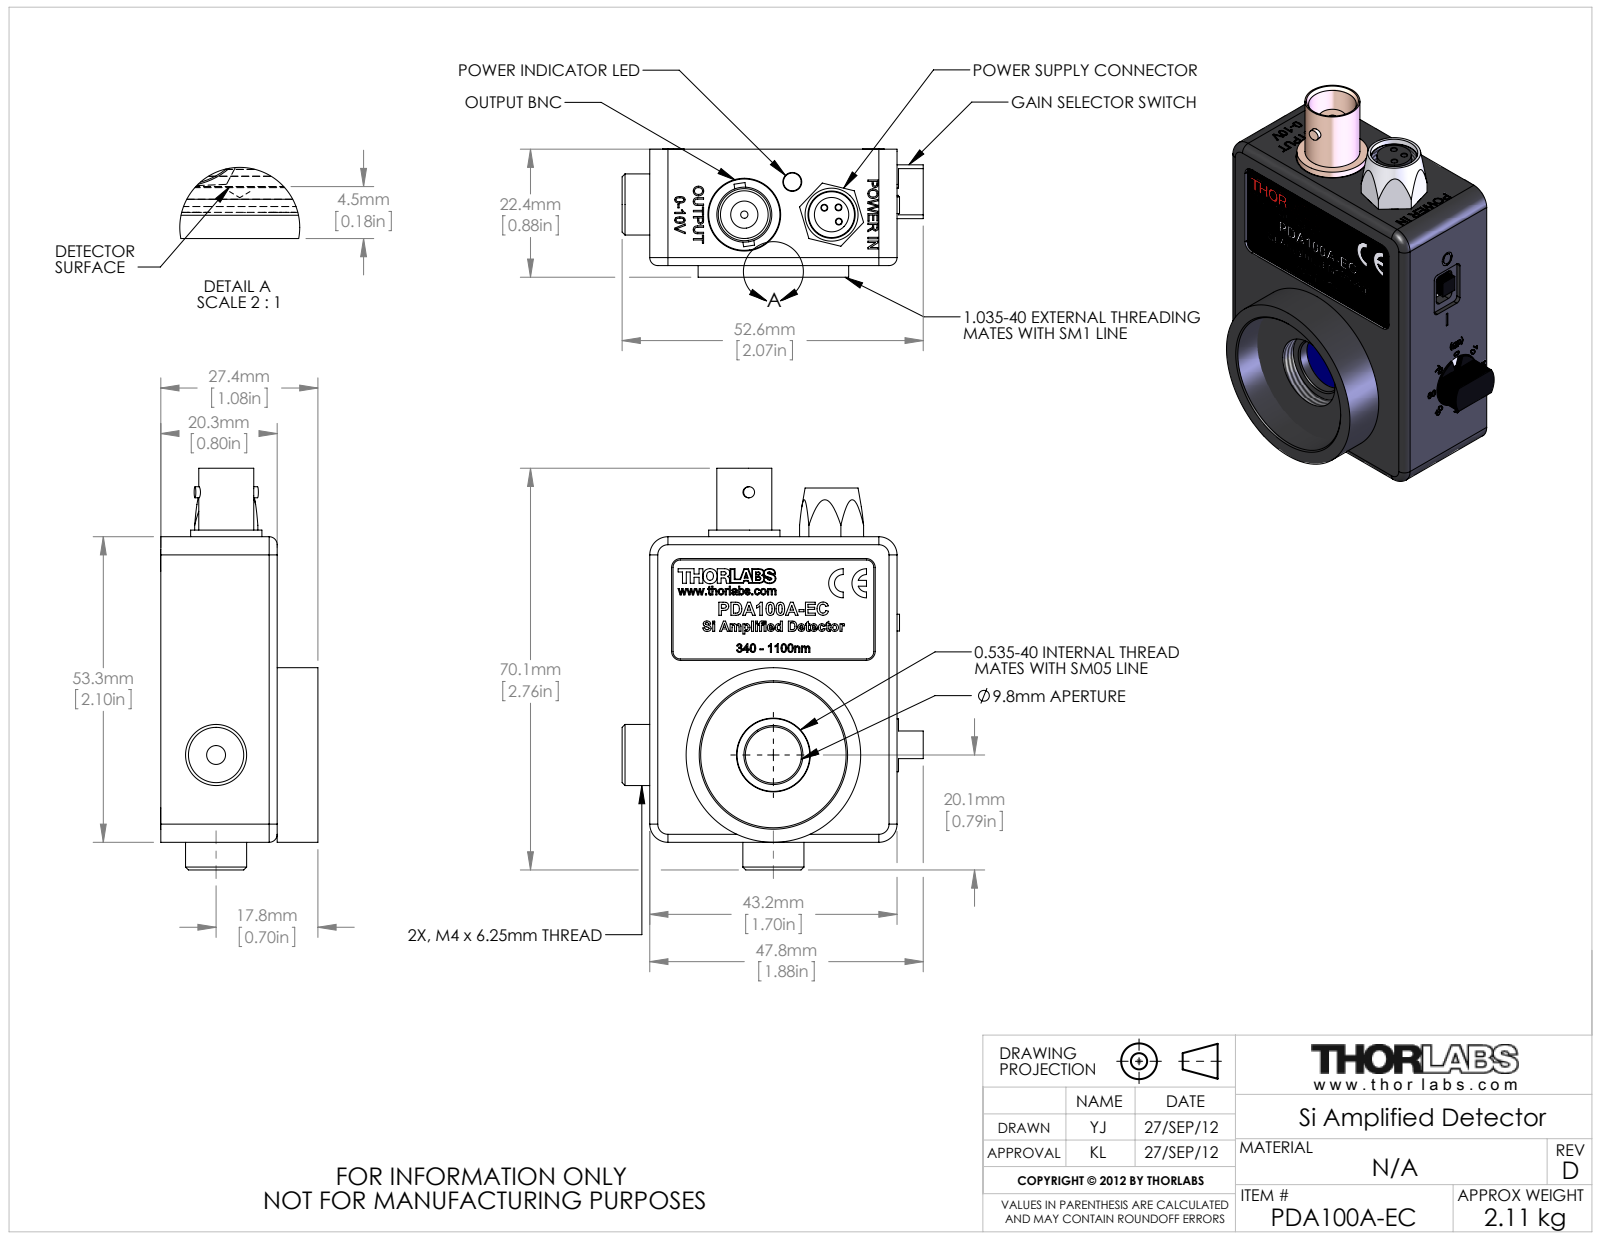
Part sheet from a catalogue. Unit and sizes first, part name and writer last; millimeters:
Units: millimetres
Overall size (bounding box): 70.12 × 52.58 × 27.47
Round holes (diameter × count): ⌀0.94 ×9, ⌀0.81 ×8, ⌀1.78 ×7, ⌀2.44 ×6, ⌀3.17 ×4, ⌀5.08 ×4, ⌀1 ×3, ⌀1.27 ×3, ⌀0.64 ×2, ⌀1.14 ×2, ⌀3.3 ×2, ⌀3.81 ×2
Round bosses / shafts (diameter × count): ⌀2.18 ×7, ⌀3.73 ×4, ⌀3.56 ×3, ⌀1.6 ×3, ⌀13.97 ×2, ⌀10.67 ×2, ⌀9.4 ×2, ⌀5.99 ×2
Partial cylindrical surfaces — rounded edges, fillets, slot ends (radius × count): R0.2 ×36, R3.17 ×23, R0.1 ×16, R0.79 ×8, R2.41 ×8, R1.27 ×5, R1.4 ×4, R1.59 ×4
Main face-to-face distances: 1.59, 2.54, 12.76, 14.35, 1.58, 12.77, 1.27, 11.18, 0.51, 5.77
Hole centre spacings: 2.54, 2, 3.2, 3.25, 3.59, 5.15, 7.11, 1.75
Volume: 25 449 mm³ · Surface area: 29 896 mm²
Bodies: 48 solids, 3458 faces (1697 planar, 837 cylindrical, 924 other)
Part name (STEP PRODUCT): 14027-E0W
STEP written by: SolidWorks 2011 (AUTOMOTIVE_DESIGN)
